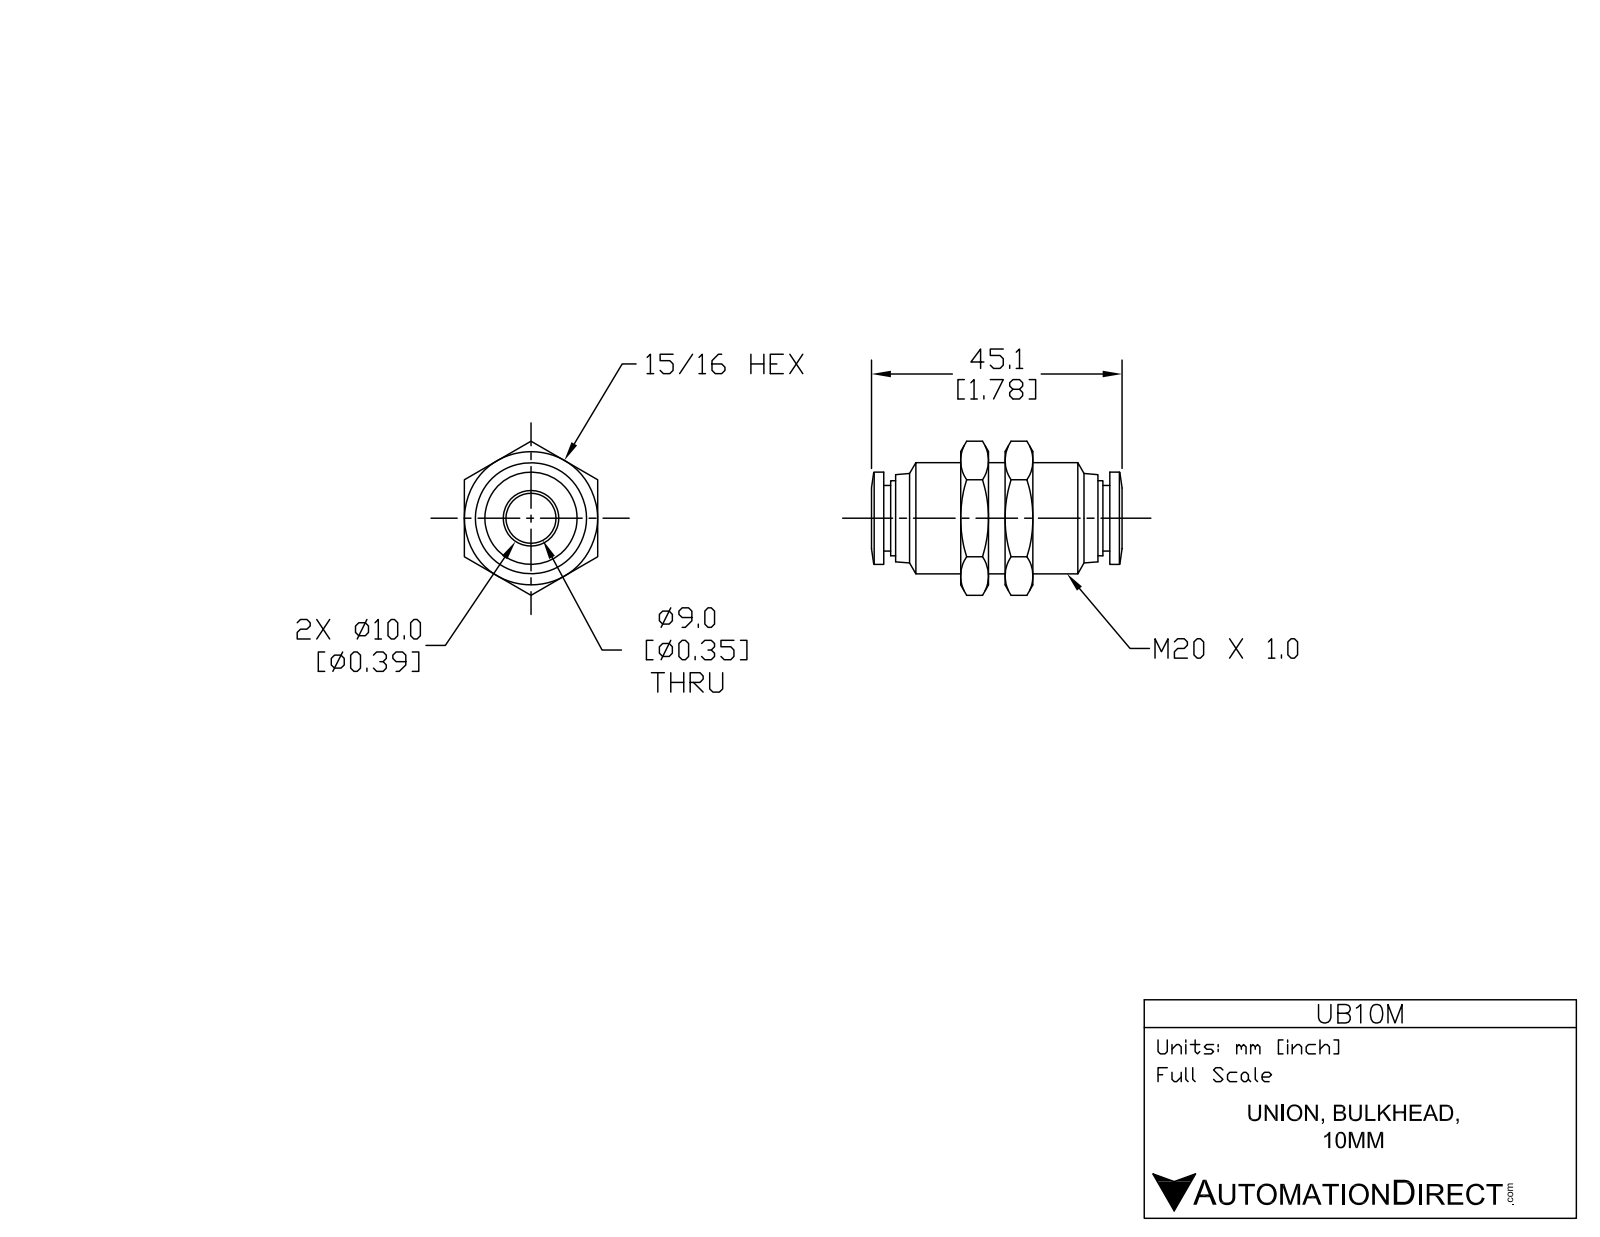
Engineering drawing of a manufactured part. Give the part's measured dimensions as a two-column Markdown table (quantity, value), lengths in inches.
| quantity | value |
| --- | --- |
| part name | UB10M |
| STEP written by | SolidWorks 2015 (AUTOMOTIVE_DESIGN) |
| units | inches |
| bodies | 1 solid, 98 faces (26 planar, 24 cylindrical, 48 other) |
| overall size | 1.776 × 1.091 × 0.945 |
| volume | 0.629 in³ |
| surface area | 8.768 in² |
| round holes (diameter × count) | 0.354 × 1, 0.406 × 1 |
| round bosses / shafts (diameter × count) | 0.787 × 1, 0.654 × 1, 0.531 × 1, 0.465 × 1 |
| main face-to-face distances | 0.945, 0.197, 0.315, 0.545, 0.742, 0.86, 1.057, 0.118, 0.512, 1.602 |
